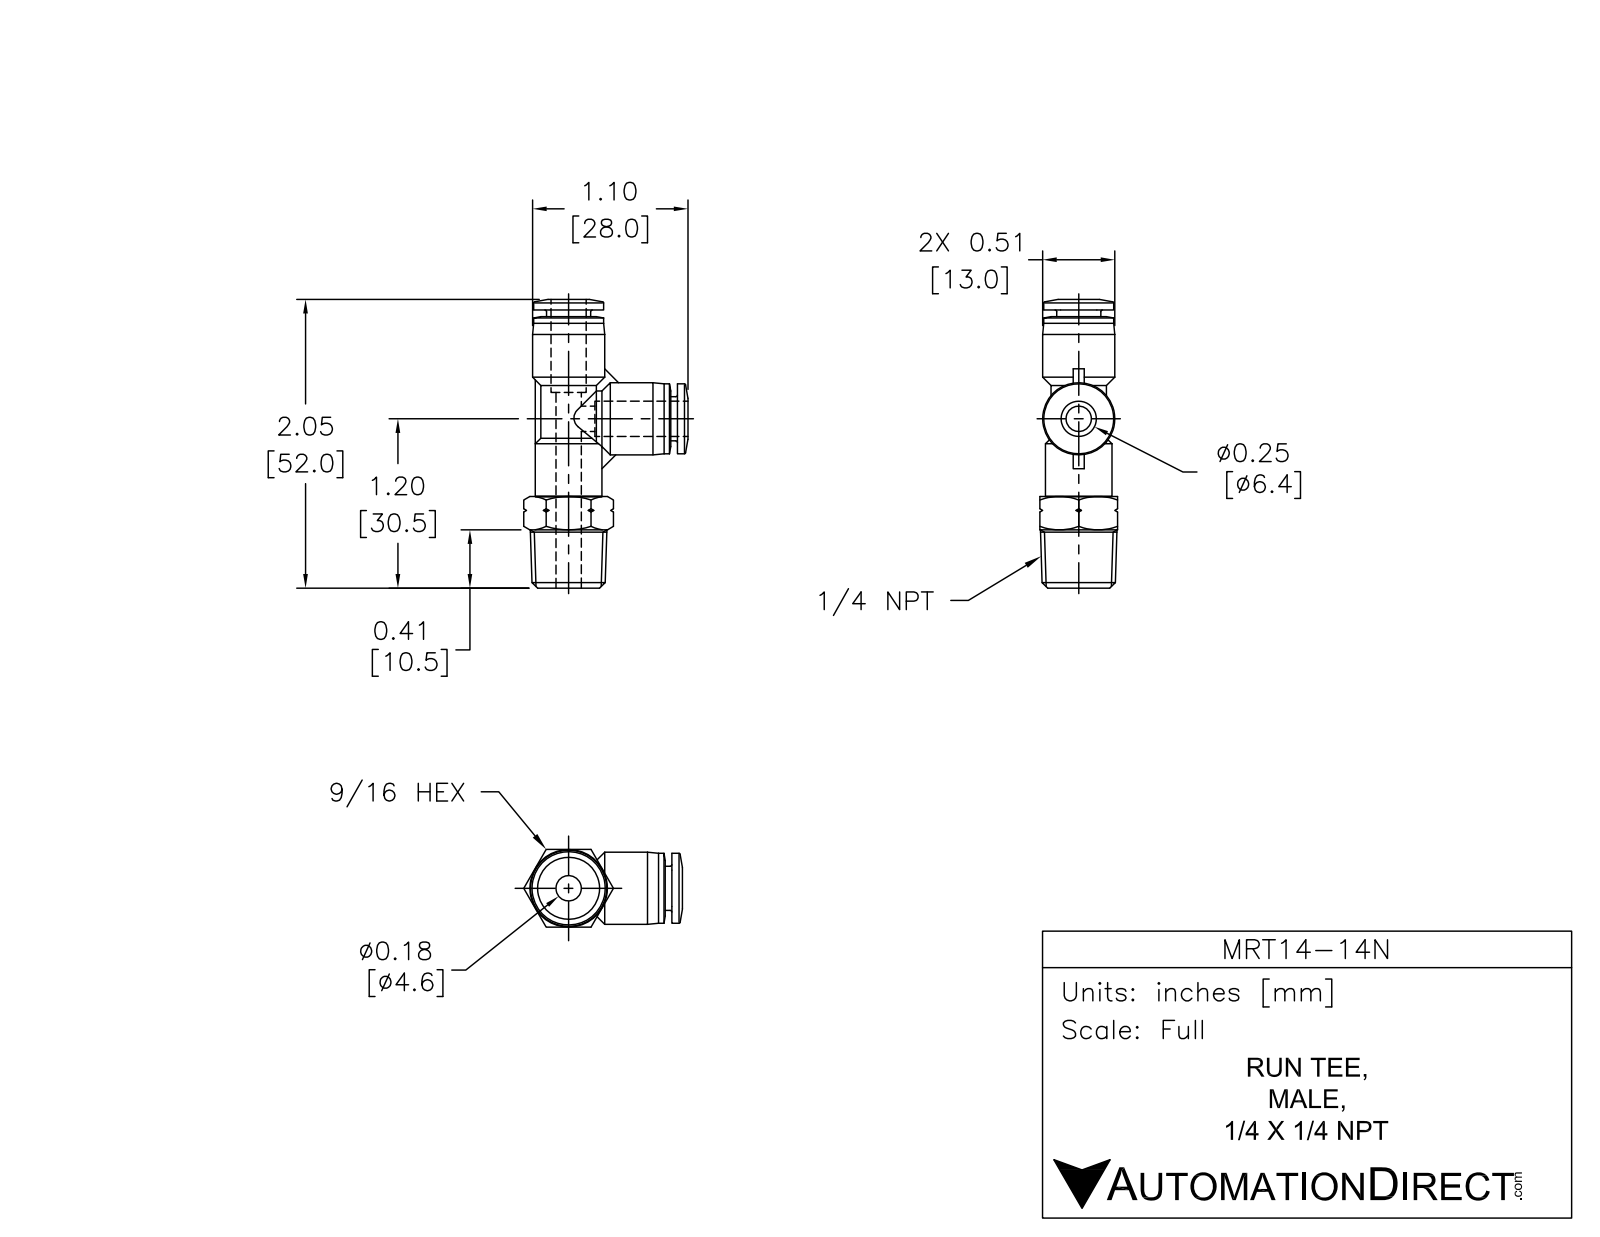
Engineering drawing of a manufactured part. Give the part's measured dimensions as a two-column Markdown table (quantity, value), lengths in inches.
| quantity | value |
| --- | --- |
| part name | MRT14-14N |
| STEP written by | SolidWorks 2015 (AUTOMOTIVE_DESIGN) |
| units | inches |
| bodies | 1 solid, 119 faces (23 planar, 30 cylindrical, 66 other) |
| overall size | 2.047 × 1.165 × 0.551 |
| volume | 0.408 in³ |
| surface area | 6.929 in² |
| round holes (diameter × count) | 0.157 × 2, 0.258 × 2 |
| round bosses / shafts (diameter × count) | 0.512 × 2, 0.496 × 2, 0.394 × 2, 0.313 × 2, 0.472 × 1 |
| main face-to-face distances | 0.551, 1.972, 0.047, 0.236, 0.315, 0.539, 0.587, 0.65, 1.323, 1.925 |
